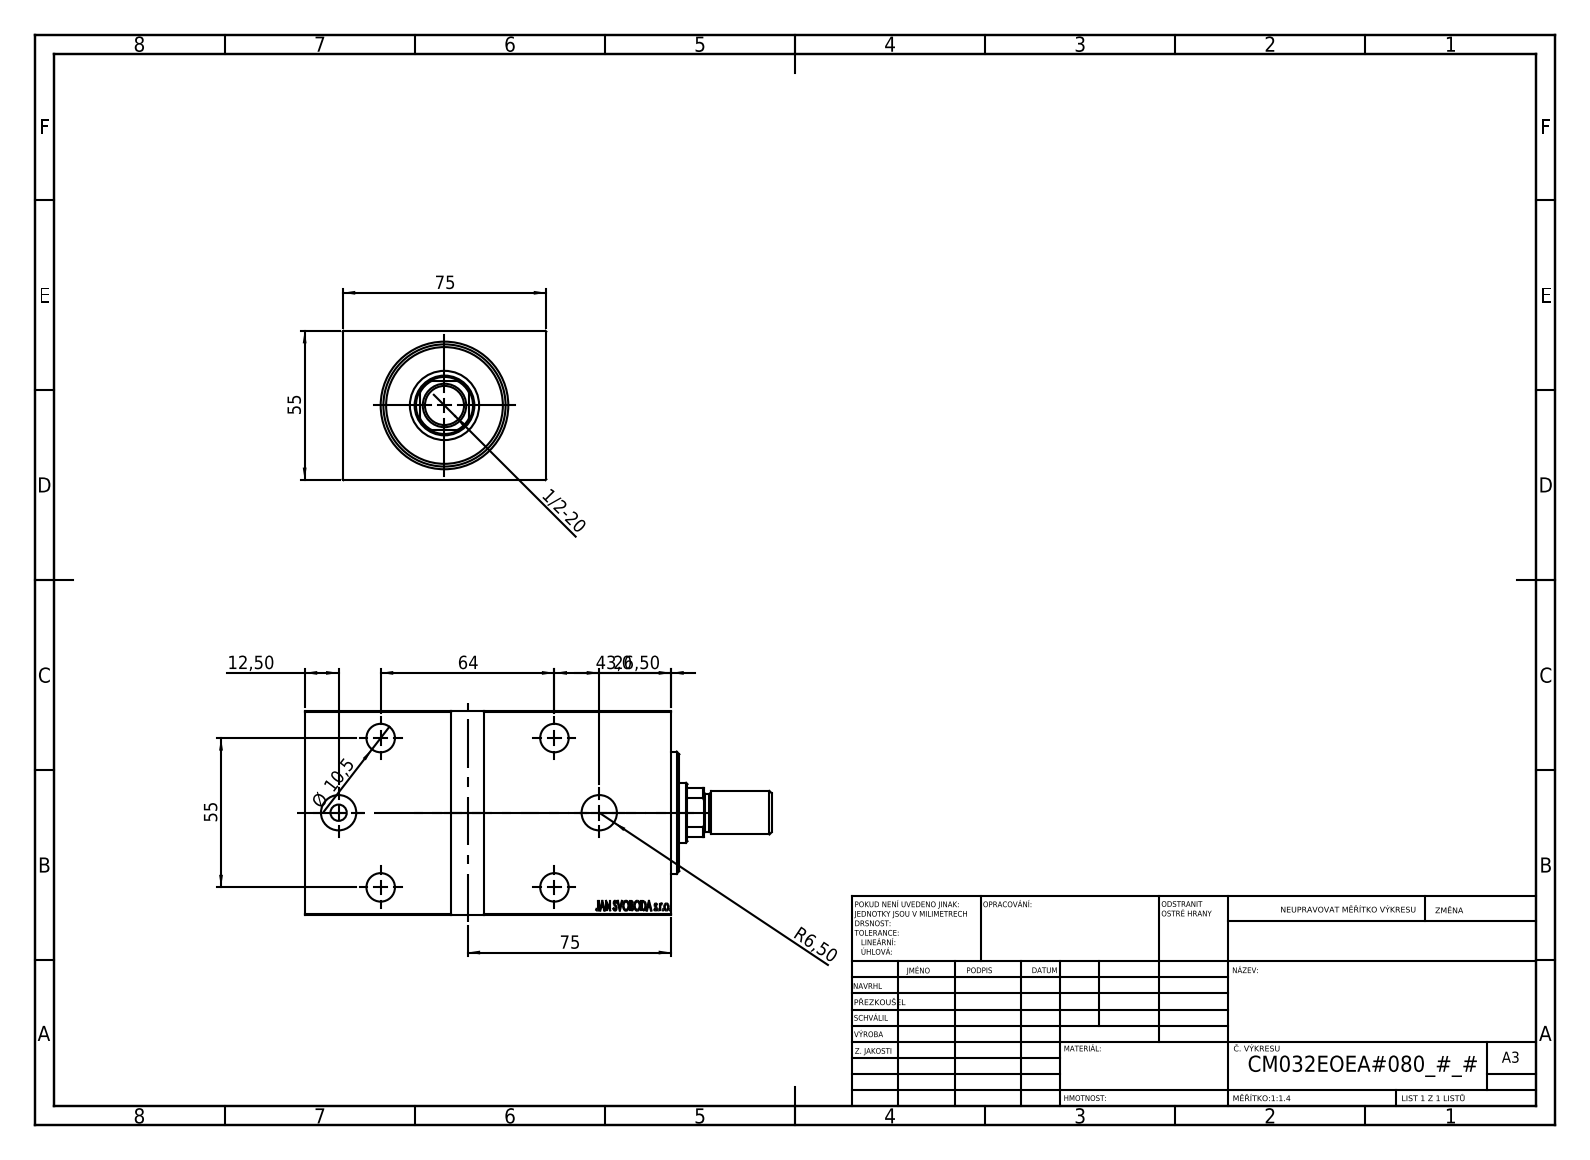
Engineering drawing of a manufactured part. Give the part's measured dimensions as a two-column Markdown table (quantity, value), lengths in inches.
| quantity | value |
| --- | --- |
| part name | V450CM_MALE_METRIC; V450CM_VC_B; V450CM_E_Body; V450CM_E_VCP |
| STEP written by | SolidWorks 2019 (CONFIG_CONTROL_DESIGN) |
| units | inches |
| bodies | 4 solids, 859 faces (411 planar, 48 cylindrical, 400 other) |
| overall size | 6.772 × 2.953 × 2.165 |
| volume | 30.92 in³ |
| surface area | 131.3 in² |
| round holes (diameter × count) | 0.413 × 5, 0.65 × 4, 0.512 × 2, 0.866 × 1, 1.004 × 1, 1.26 × 1, 1.772 × 1 |
| round bosses / shafts (diameter × count) | 1.339 × 1, 0.63 × 1, 0.551 × 1, 0.236 × 1 |
| partial cylindrical surfaces (radius × count) | 0.413 × 1 |
| main face-to-face distances | 2.165, 2.953, 5.315, 0.118, 0.394, 4.921, 0.197, 5.118, 4.724, 5.433 |
| hole center spacings | 1.243, 1.263, 2.165, 2.52, 3.312, 3.322, 3.349, 3.78 |
